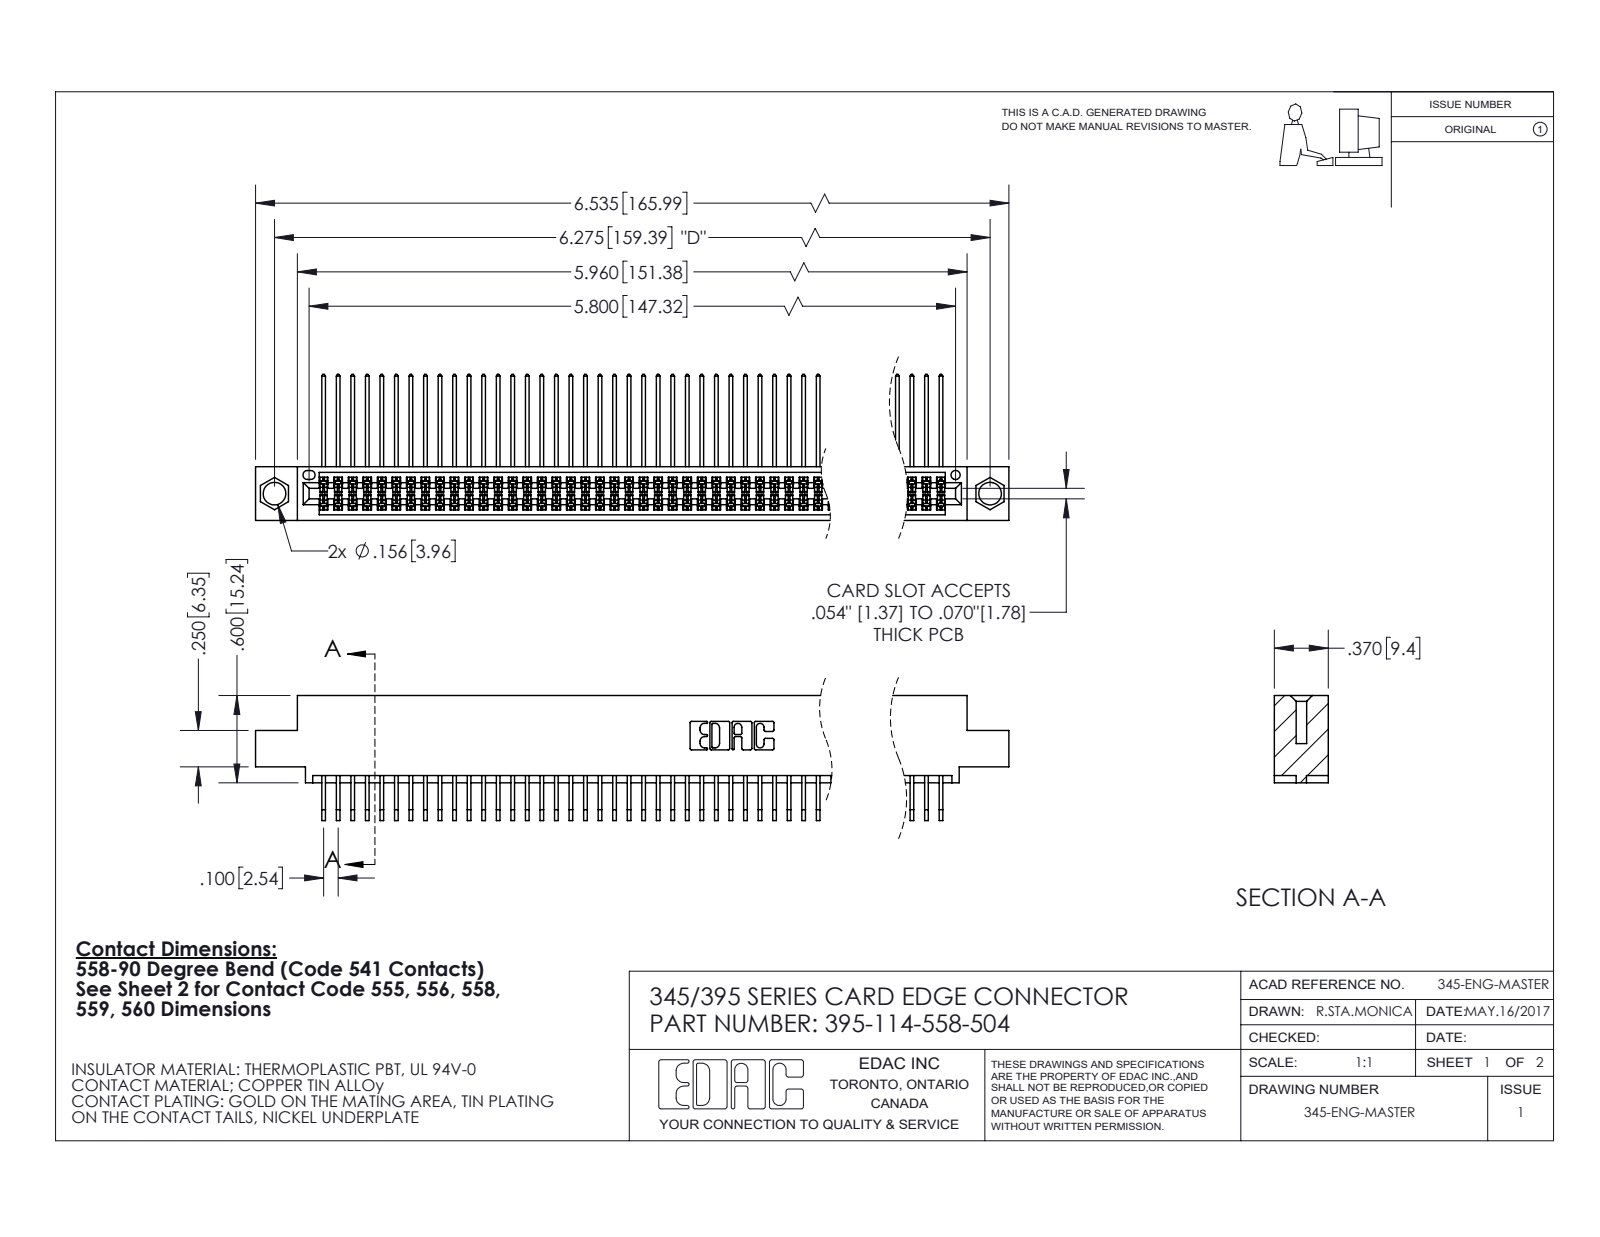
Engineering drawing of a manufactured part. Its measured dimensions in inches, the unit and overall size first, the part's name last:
Units: inches
Overall size (bounding box): 6.535 × 1.005 × 0.859
Round holes (diameter × count): ⌀0.156 ×2, ⌀0.064 ×1
Partial cylindrical surfaces — rounded edges, fillets, slot ends (radius × count): R0.006 ×227, R0.01 ×22, R0.007 ×6, R0.031 ×6, R0.026 ×3, R0.014 ×2, R0.019 ×2, R0.022 ×2
Main face-to-face distances: 0.072, 0.298, 0.2, 0.37, 0.098, 0.272, 0.025, 0.225, 0.025, 0.175
Hole centre spacings: 0.27, 6.039, 6.275
Volume: 1.022 in³ · Surface area: 43.52 in²
Bodies: 115 solids, 6072 faces (4088 planar, 1984 cylindrical, 0 other)
Part name (STEP PRODUCT): 395-114-558-504; 345-292-001_558 559 Tail - 1; 345 Part_0.110 Offset - 0.156 Dia-TI; 345-292-001_558 Tail - 2
STEP written by: SolidWorks 2020 (CONFIG_CONTROL_DESIGN)
